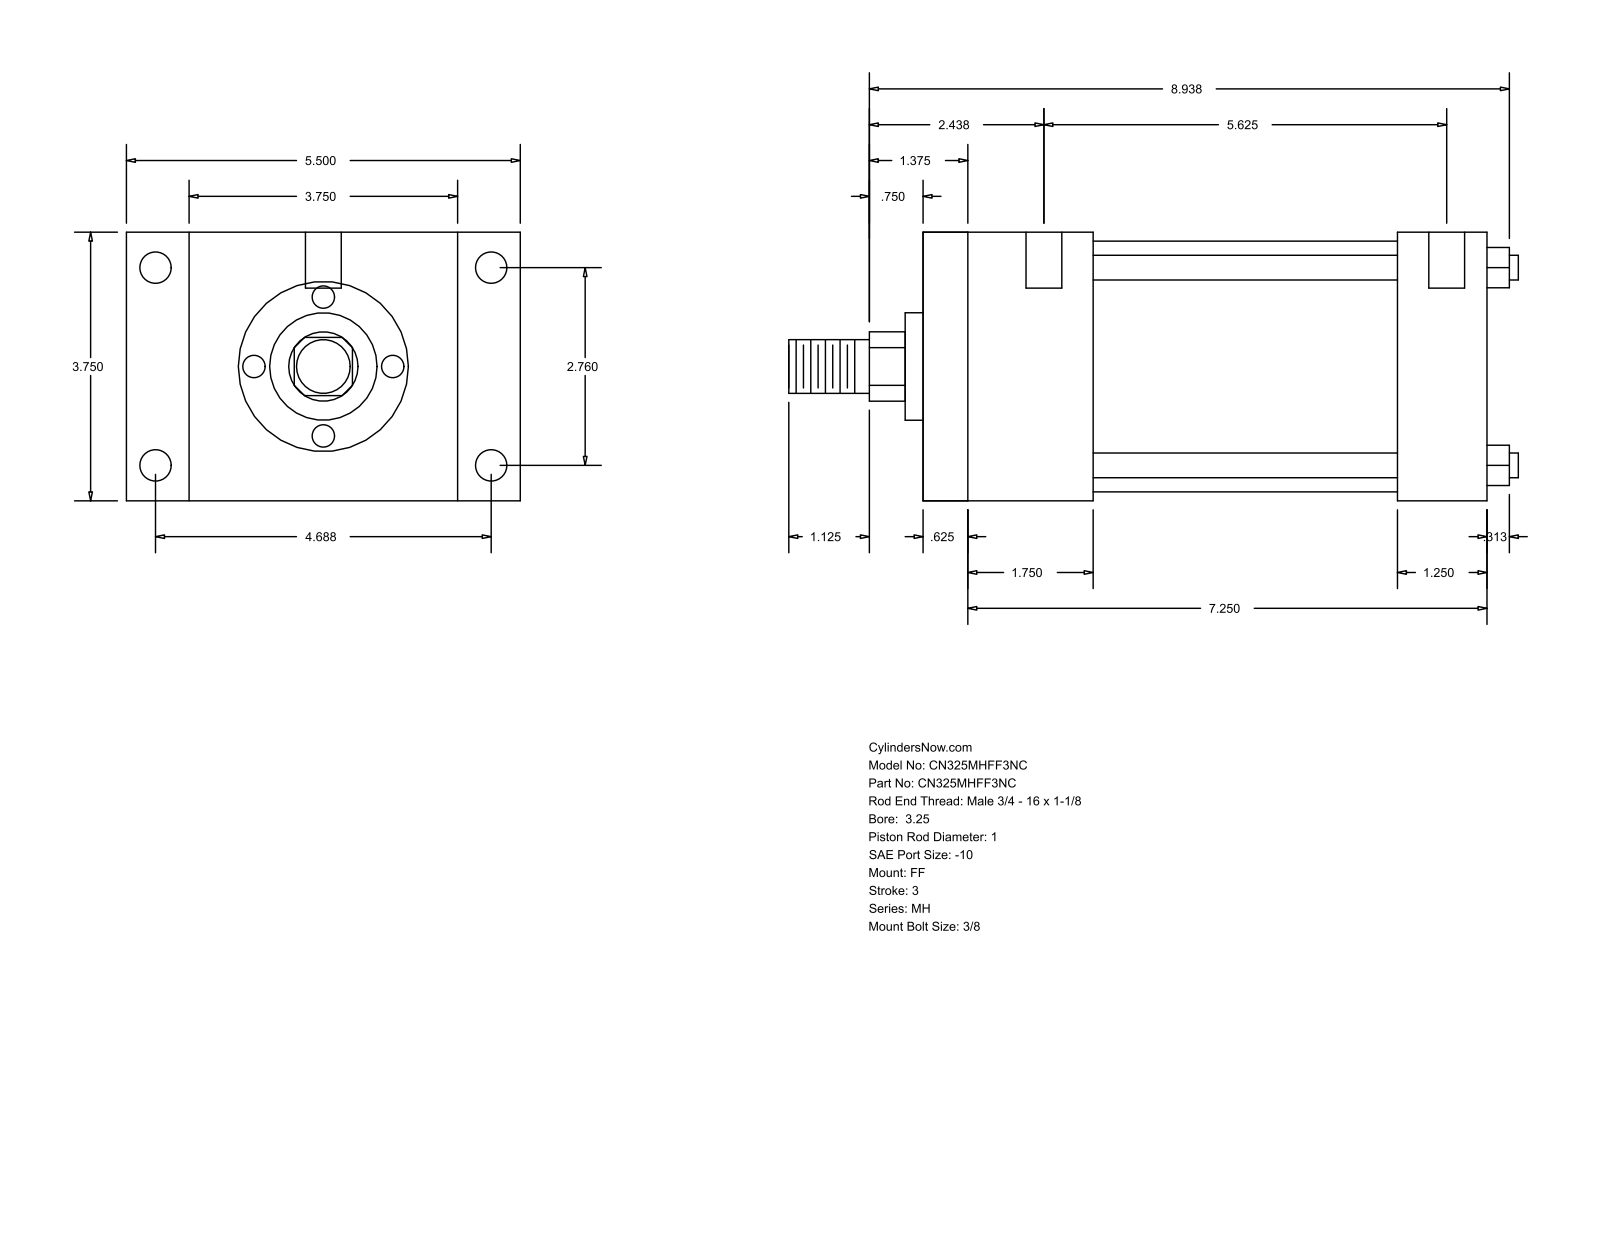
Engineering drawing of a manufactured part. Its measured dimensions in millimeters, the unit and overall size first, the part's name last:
Units: millimetres
Overall size (bounding box): 258.76 × 139.7 × 95.25
Round holes (diameter × count): ⌀5.56 ×4, ⌀11.13 ×4, ⌀12.7 ×2
Round bosses / shafts (diameter × count): ⌀8.76 ×4, ⌀88.9 ×1, ⌀38.1 ×1, ⌀25.4 ×1, ⌀19.05 ×1
Partial cylindrical surfaces — rounded edges, fillets, slot ends (radius × count): R12.29 ×1
Main face-to-face distances: 95.24, 200.02, 15.87, 184.15, 22.23, 117.47, 168.27, 152.4, 31.75, 60.33
Hole centre spacings: 70.1, 119.06, 138.16, 149.22, 1.58, 4.76, 142.88, 144.46
Bodies: 0 solids, 92 faces (64 planar, 28 cylindrical, 0 other)
Part name (STEP PRODUCT): MH_FF__0325_1
STEP written by: GSSL Pune (CONFIG_CONTROL_DESIGN)
